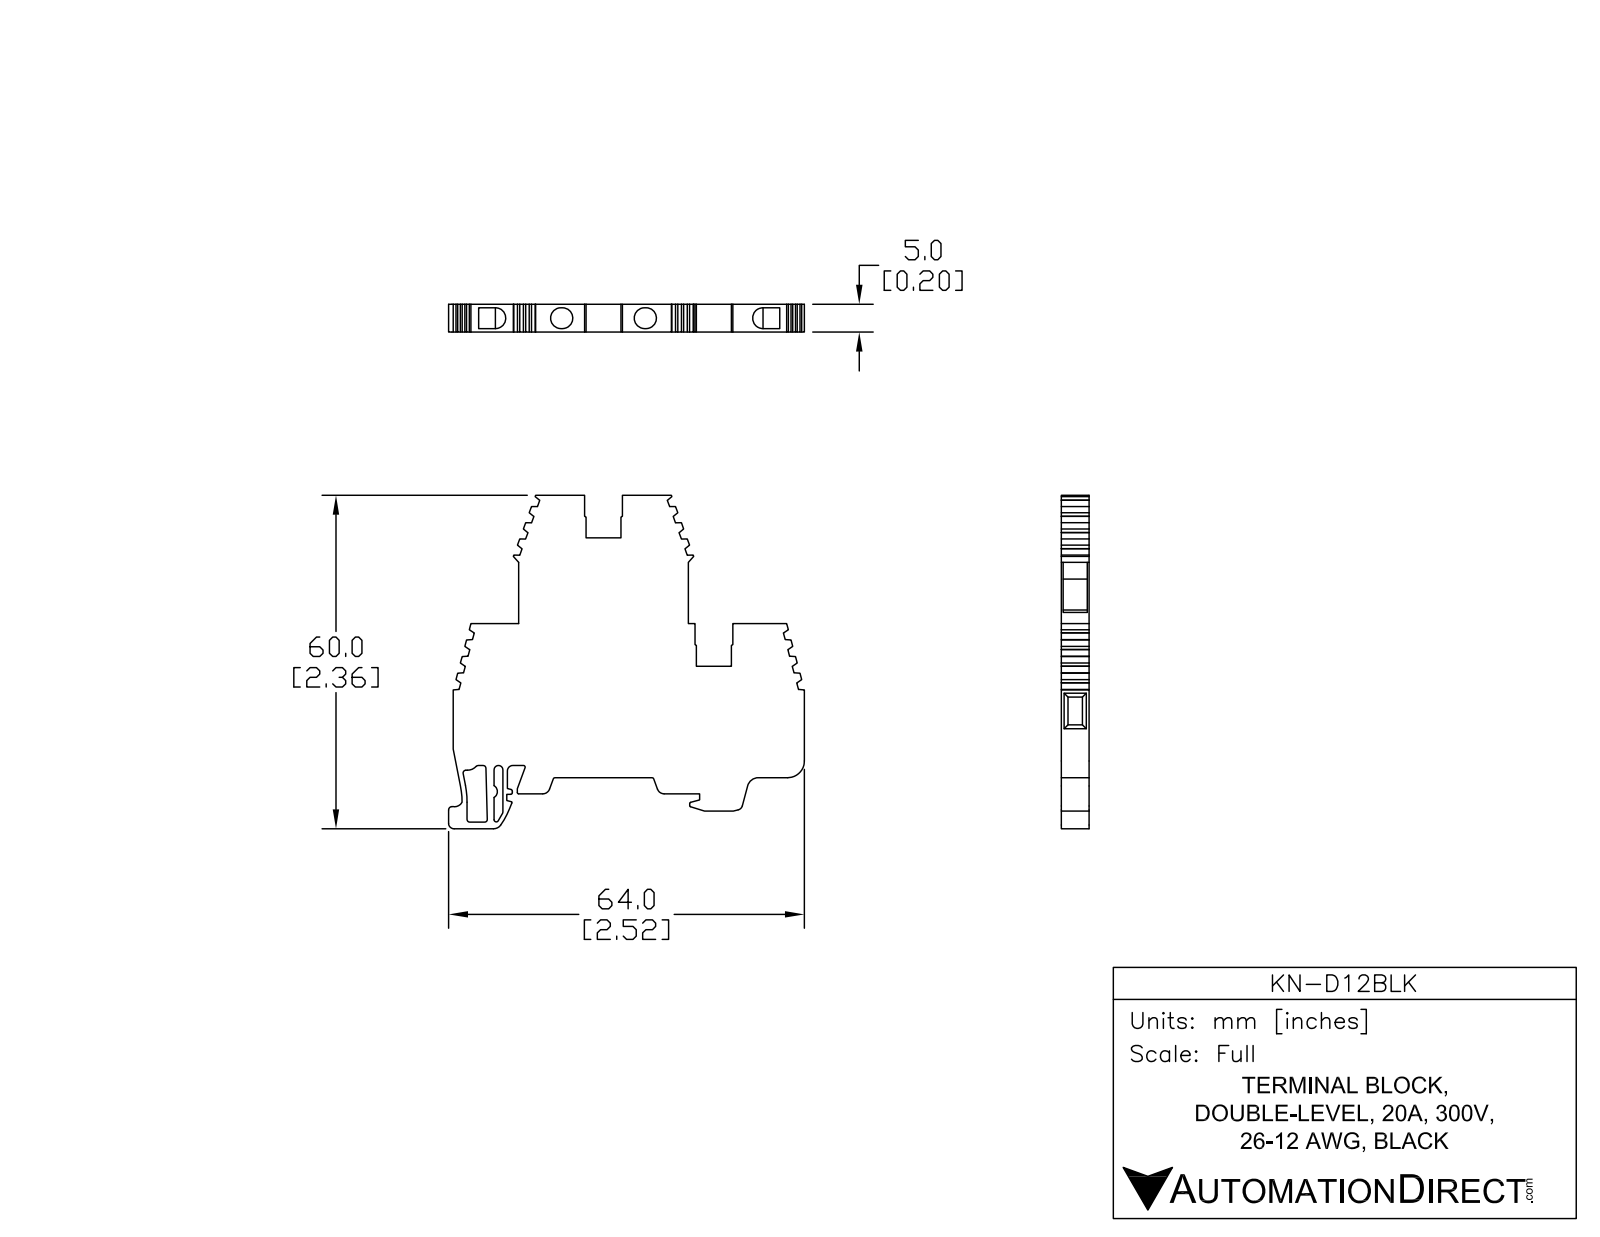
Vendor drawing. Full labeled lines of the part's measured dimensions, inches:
Part name (STEP PRODUCT): KN-D12
STEP written by: SolidWorks 2014 (AUTOMOTIVE_DESIGN)
Units: inches
Bodies: 1 solid, 239 faces (196 planar, 43 cylindrical, 0 other)
Overall size (bounding box): 2.521 × 2.362 × 0.197
Volume: 0.693 in³ · Surface area: 10.9 in²
Partial cylindrical surfaces — rounded edges, fillets, slot ends (radius × count): R0.02 ×7, R0.012 ×6, R0.074 ×6, R0.008 ×3, R0.039 ×3, R0.024 ×2, R0.016 ×1, R0.031 ×1
Main face-to-face distances: 0.197, 0.184, 0.013, 0.115, 0.909, 0.157, 0.258, 0.782, 0.248, 0.231
